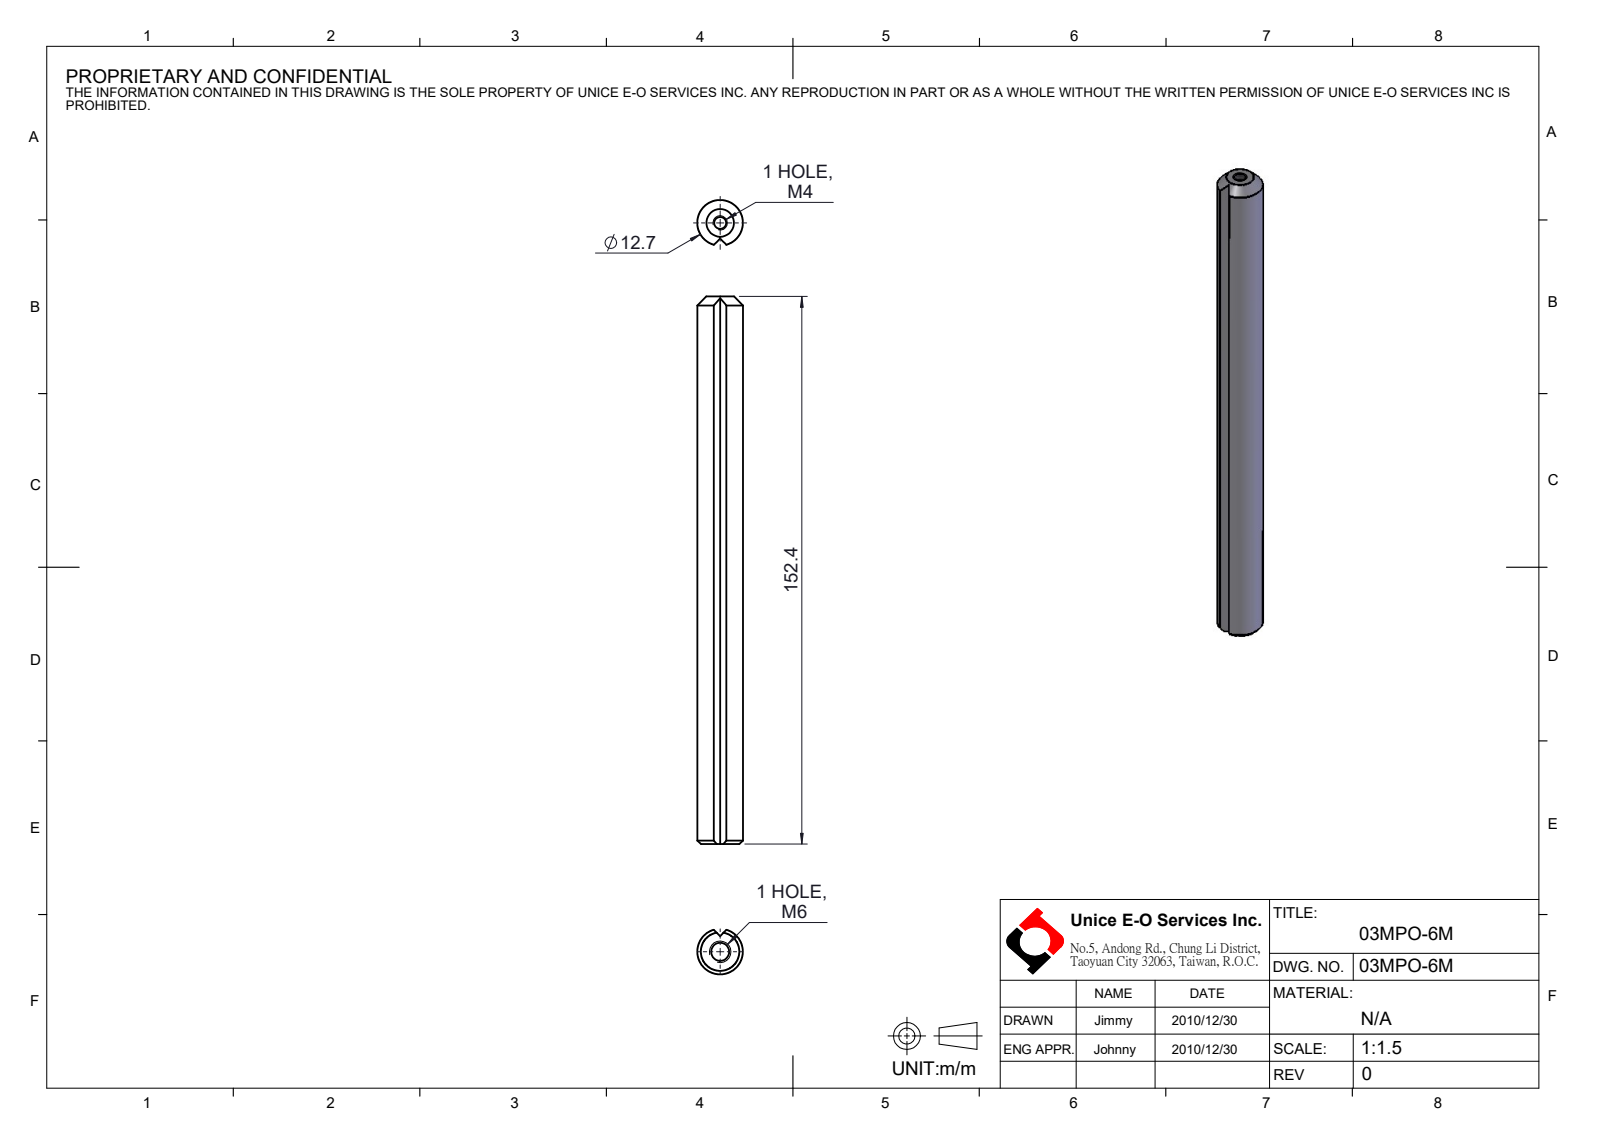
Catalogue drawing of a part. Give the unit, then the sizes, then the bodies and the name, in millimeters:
Units: millimetres
Overall size (bounding box): 152.4 × 12.7 × 12.45
Round holes (diameter × count): ⌀3.3 ×1, ⌀5 ×1
Round bosses / shafts (diameter × count): ⌀12.7 ×1
Main face-to-face distances: 152.4
Volume: 18 238 mm³ · Surface area: 6 796 mm²
Bodies: 1 solid, 17 faces (4 planar, 6 cylindrical, 7 other)
Part name (STEP PRODUCT): 03MPO-6M
STEP written by: SolidWorks 2016 (CONFIG_CONTROL_DESIGN)
